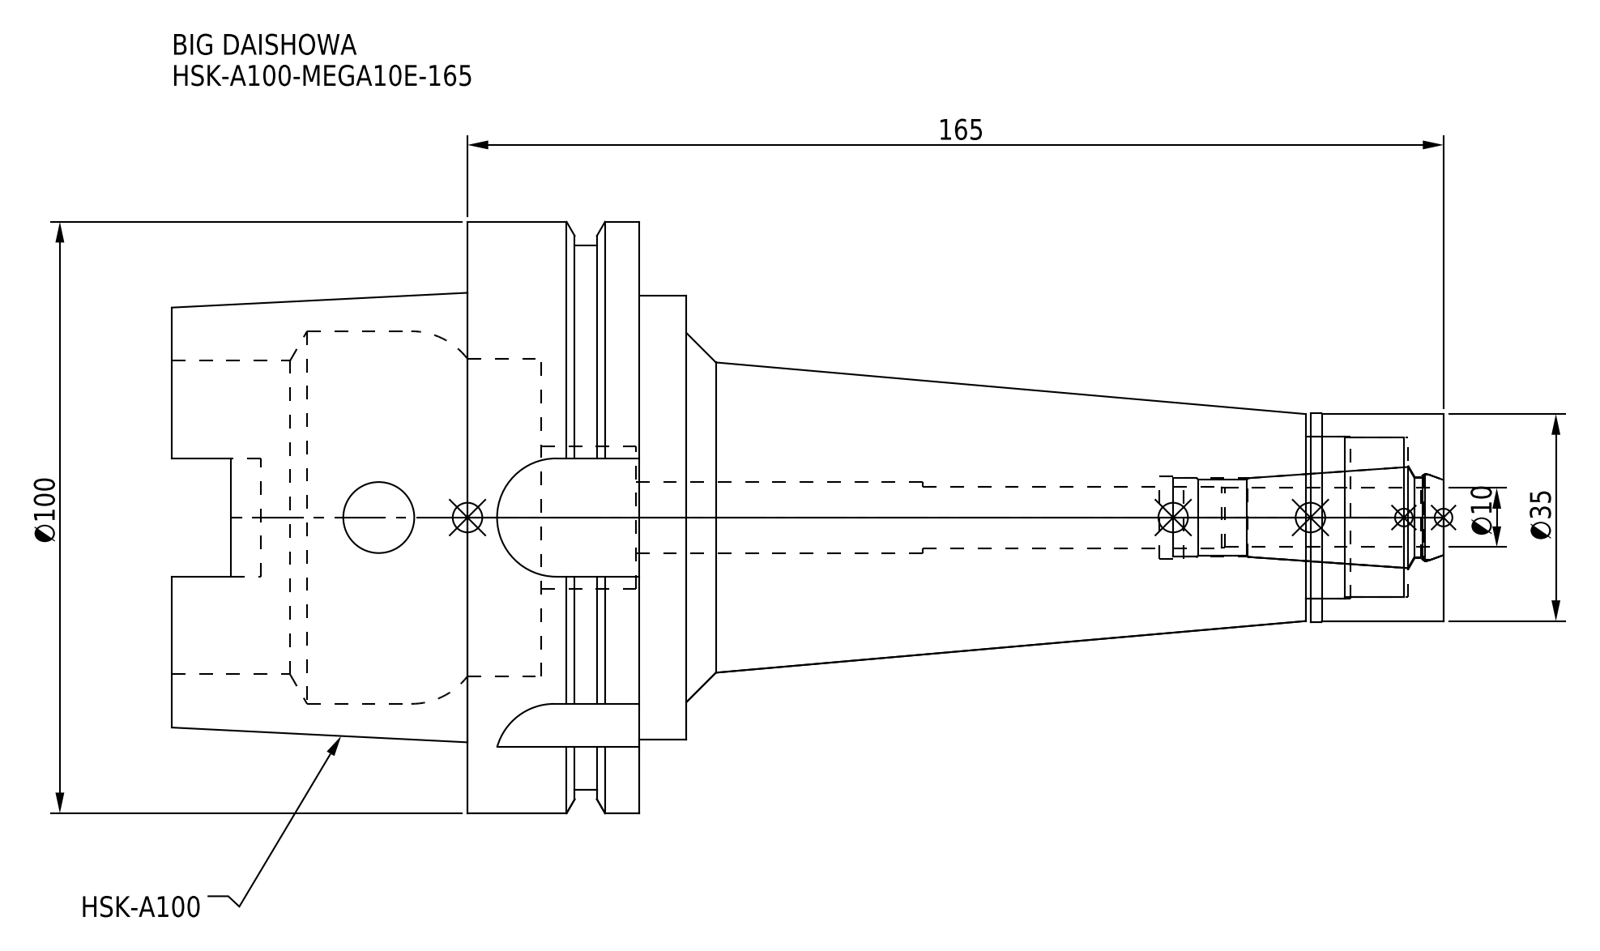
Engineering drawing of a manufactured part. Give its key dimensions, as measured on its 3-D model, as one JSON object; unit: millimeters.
{"part_name": "HSK-A100-MEGA10E-165-100.stp; MEN10_1.stp; HSK-A100-MEGA10E-165_1.stp; HSK-A100-MEGA10E-165 (+3 more)", "step_written_by": "SolidWorks 2019 (CONFIG_CONTROL_DESIGN)", "units": "millimeters", "bodies": {"solids": 2, "faces": 126, "planar": 42, "cylindrical": 56, "other": 28}, "overall_size": [215, 100, 100], "volume_mm3": 458609, "surface_area_mm2": 76822, "round_holes": [[12, 2], [10.4, 1], [13.3, 1], [13.8, 1], [13.9, 1], [14.7, 1], [24, 1], [27, 1], [27.5, 1], [53, 1], [53.8, 1], [63, 1]], "round_bosses_or_shafts": [[100, 1], [92, 1], [75, 1], [35.3, 1], [35, 1]], "partial_cylinders_radius": [[4.88, 4], [10, 4]], "face_to_face_distances": [29, 16.55, 12.45, 8, 24.55, 37, 87, 79, 62.45, 50]}
